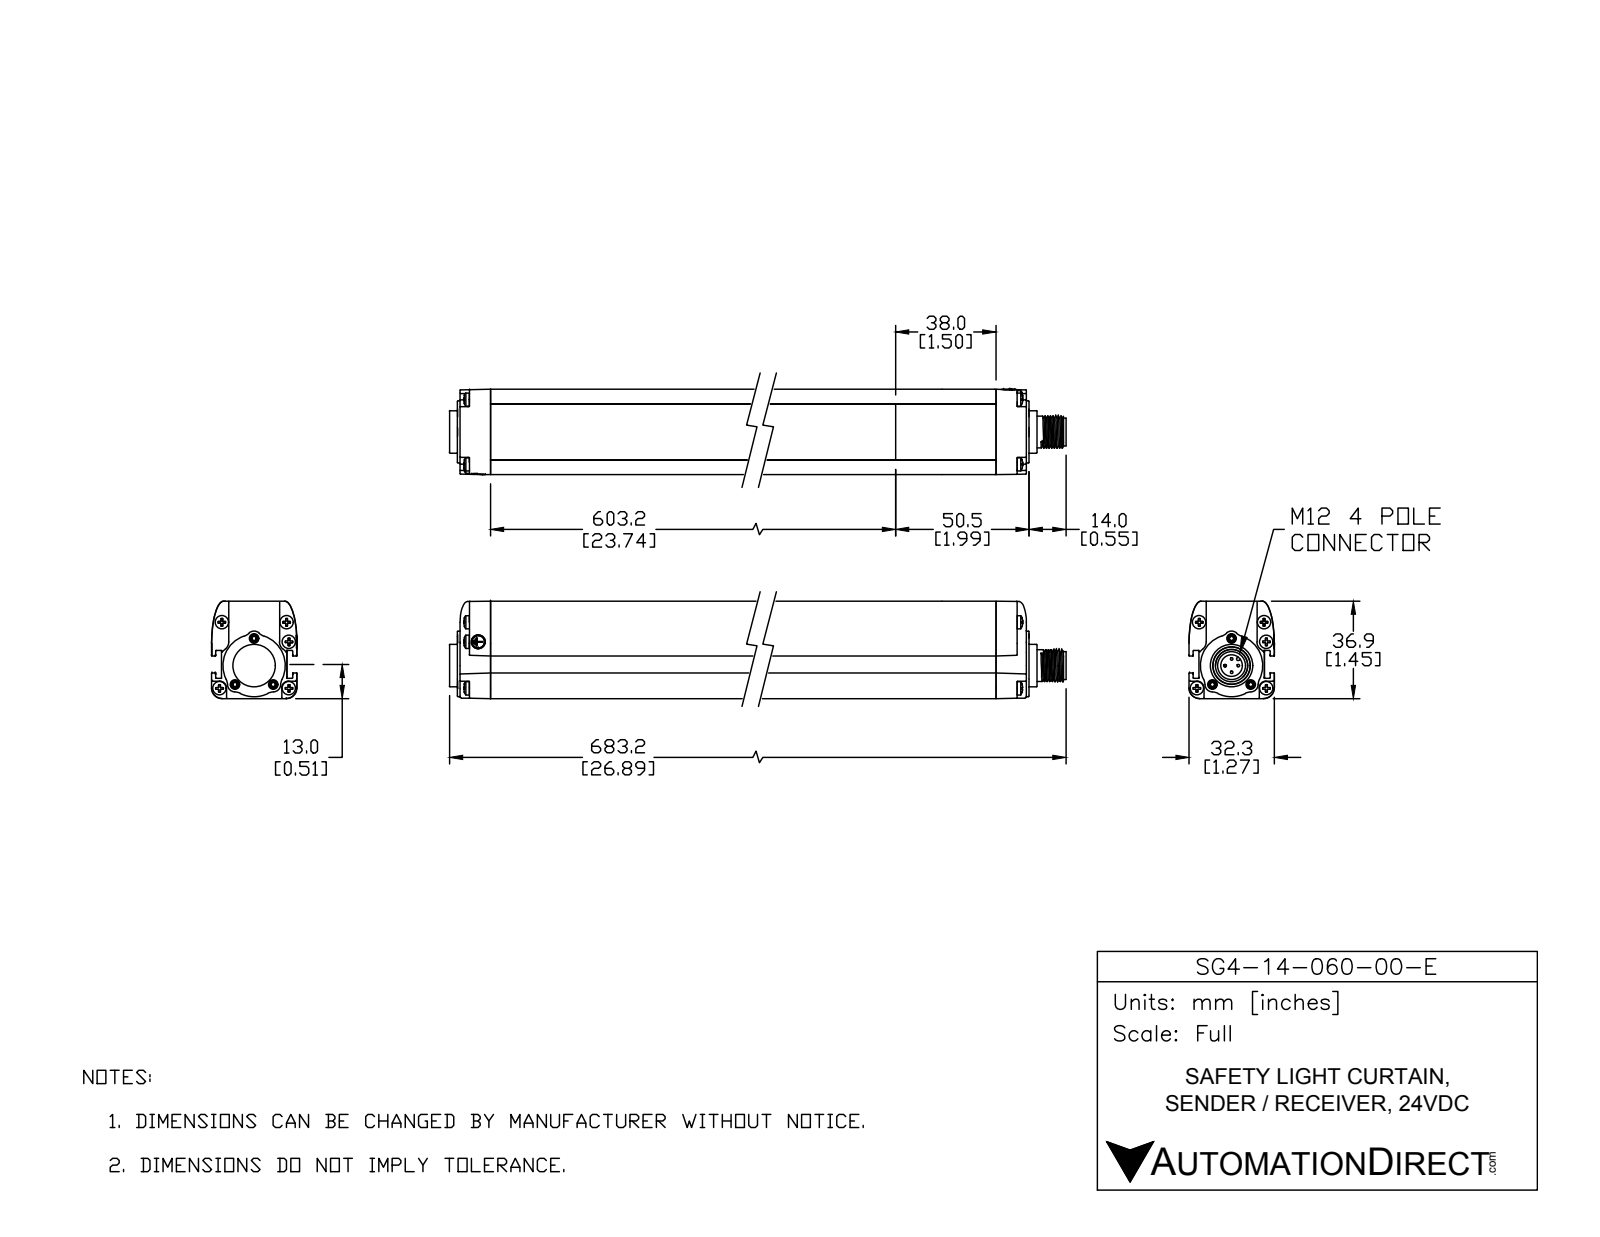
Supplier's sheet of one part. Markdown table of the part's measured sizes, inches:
| quantity | value |
| --- | --- |
| part name | SG4-14-060-OO-E |
| STEP written by | SolidWorks 2017 (AUTOMOTIVE_DESIGN) |
| units | inches |
| bodies | 29 solids, 1674 faces (410 planar, 591 cylindrical, 673 other) |
| overall size | 26.895 × 2.48 × 2.055 |
| volume | 42.79 in³ |
| surface area | 272.3 in² |
| round holes (diameter × count) | 0.106 × 6, 0.209 × 6, 0.081 × 4, 0.165 × 4, 0.26 × 4, 0.059 × 3, 0.142 × 3, 0.323 × 1, 0.376 × 1, 0.433 × 1, 0.563 × 1 |
| round bosses / shafts (diameter × count) | 0.197 × 10, 0.394 × 4, 0.039 × 4, 0.185 × 2, 0.63 × 1, 0.55 × 1, 0.472 × 1, 0.413 × 1 |
| partial cylindrical surfaces (radius × count) | 0.008 × 148, 0.004 × 120, 0.006 × 18, 0.106 × 18, 0.118 × 8, 0.197 × 7, 0.11 × 3, 0.016 × 2 |
| main face-to-face distances | 0.079, 1.272, 1.429, 0.15, 1.122, 1.35, 0.157, 0.972, 0.118, 0.333 |
| hole center spacings | 0.569, 23.665, 0.402, 0.24, 0.293, 0.52, 0.541, 0.619 |
